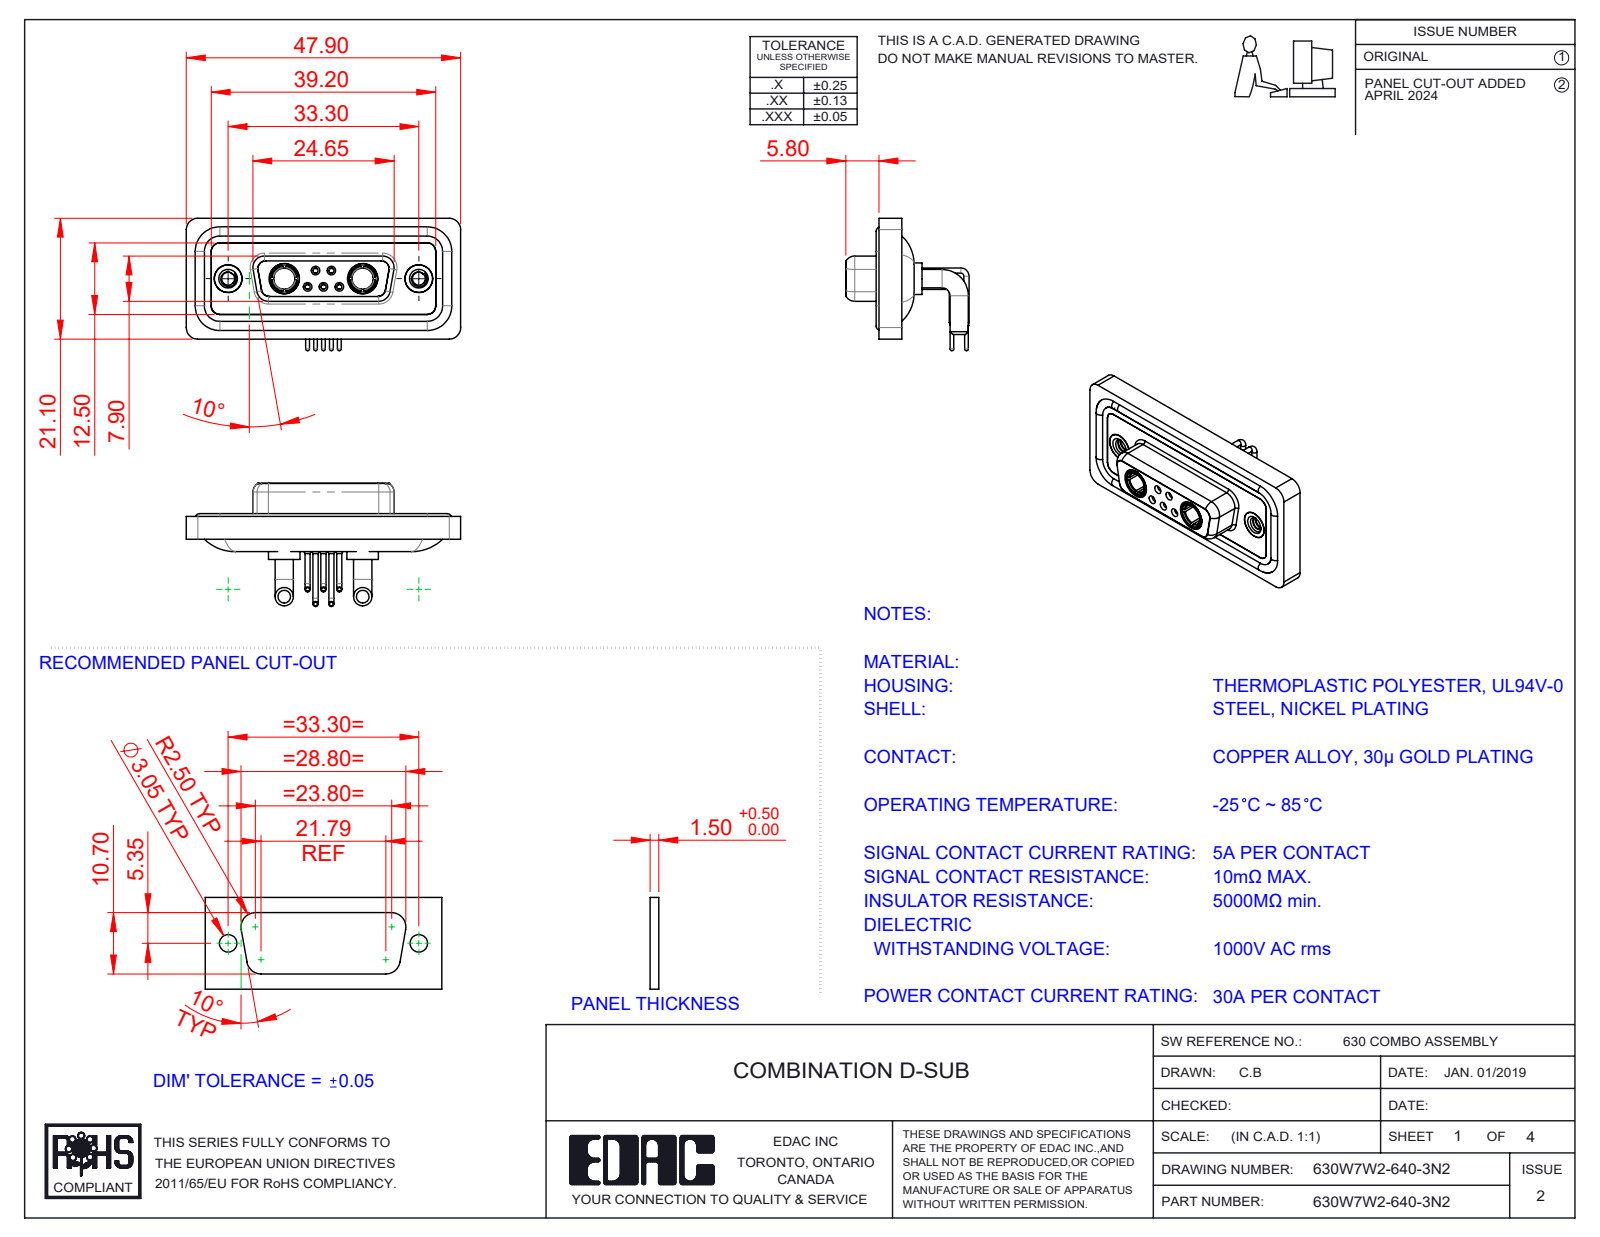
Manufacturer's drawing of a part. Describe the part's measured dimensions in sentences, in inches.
The part is named "630Combo Threaded Rivet_2; 630W7W2-640-3N2; 630Combo Shell Front_15 Contacts; 630Combo Contact Row 2_50 Contacts (+5 more)". Its 3-D file was written by "SolidWorks 2023 (CONFIG_CONTROL_DESIGN)". It is 16 solids with 807 faces: 238 planar, 353 cylindrical and 216 other. Overall it measures 1.886 by 0.91 by 0.848 inches. Its volume is 0.382 cubic inches and its surface area 15.88 square inches. Round holes: 5 of diameter 0.035, 5 of diameter 0.043, 5 of diameter 0.059, 5 of diameter 0.079, 4 of diameter 0.191, 3 of diameter 0.063, 2 of diameter 0.067, 2 of diameter 0.089, 2 of diameter 0.146, 2 of diameter 0.157, 2 of diameter 0.159, 2 of diameter 0.197. Round bosses or shafts: 6 of diameter 0.063, 5 of diameter 0.035, 5 of diameter 0.026, 4 of diameter 0.126, 2 of diameter 0.217, 2 of diameter 0.205, 2 of diameter 0.195, 2 of diameter 0.195. Partial cylindrical surfaces (rounded edges, fillets, slot ends): 20 of radius 0.079, 18 of radius 0.059, 12 of radius 0.053, 8 of radius 0.063, 4 of radius 0.01, 4 of radius 0.02, 4 of radius 0.024, 4 of radius 0.026. The main face-to-face distances are 0.016, 0.071, 0.043, 0.063, 0.098, 0.114, 0.122, 0.146, 0.161, 0.059. The hole center spacings are 0.124, 0.109, 0.386, 0.925, 0.17, 0.17, 0.198, 0.198.
